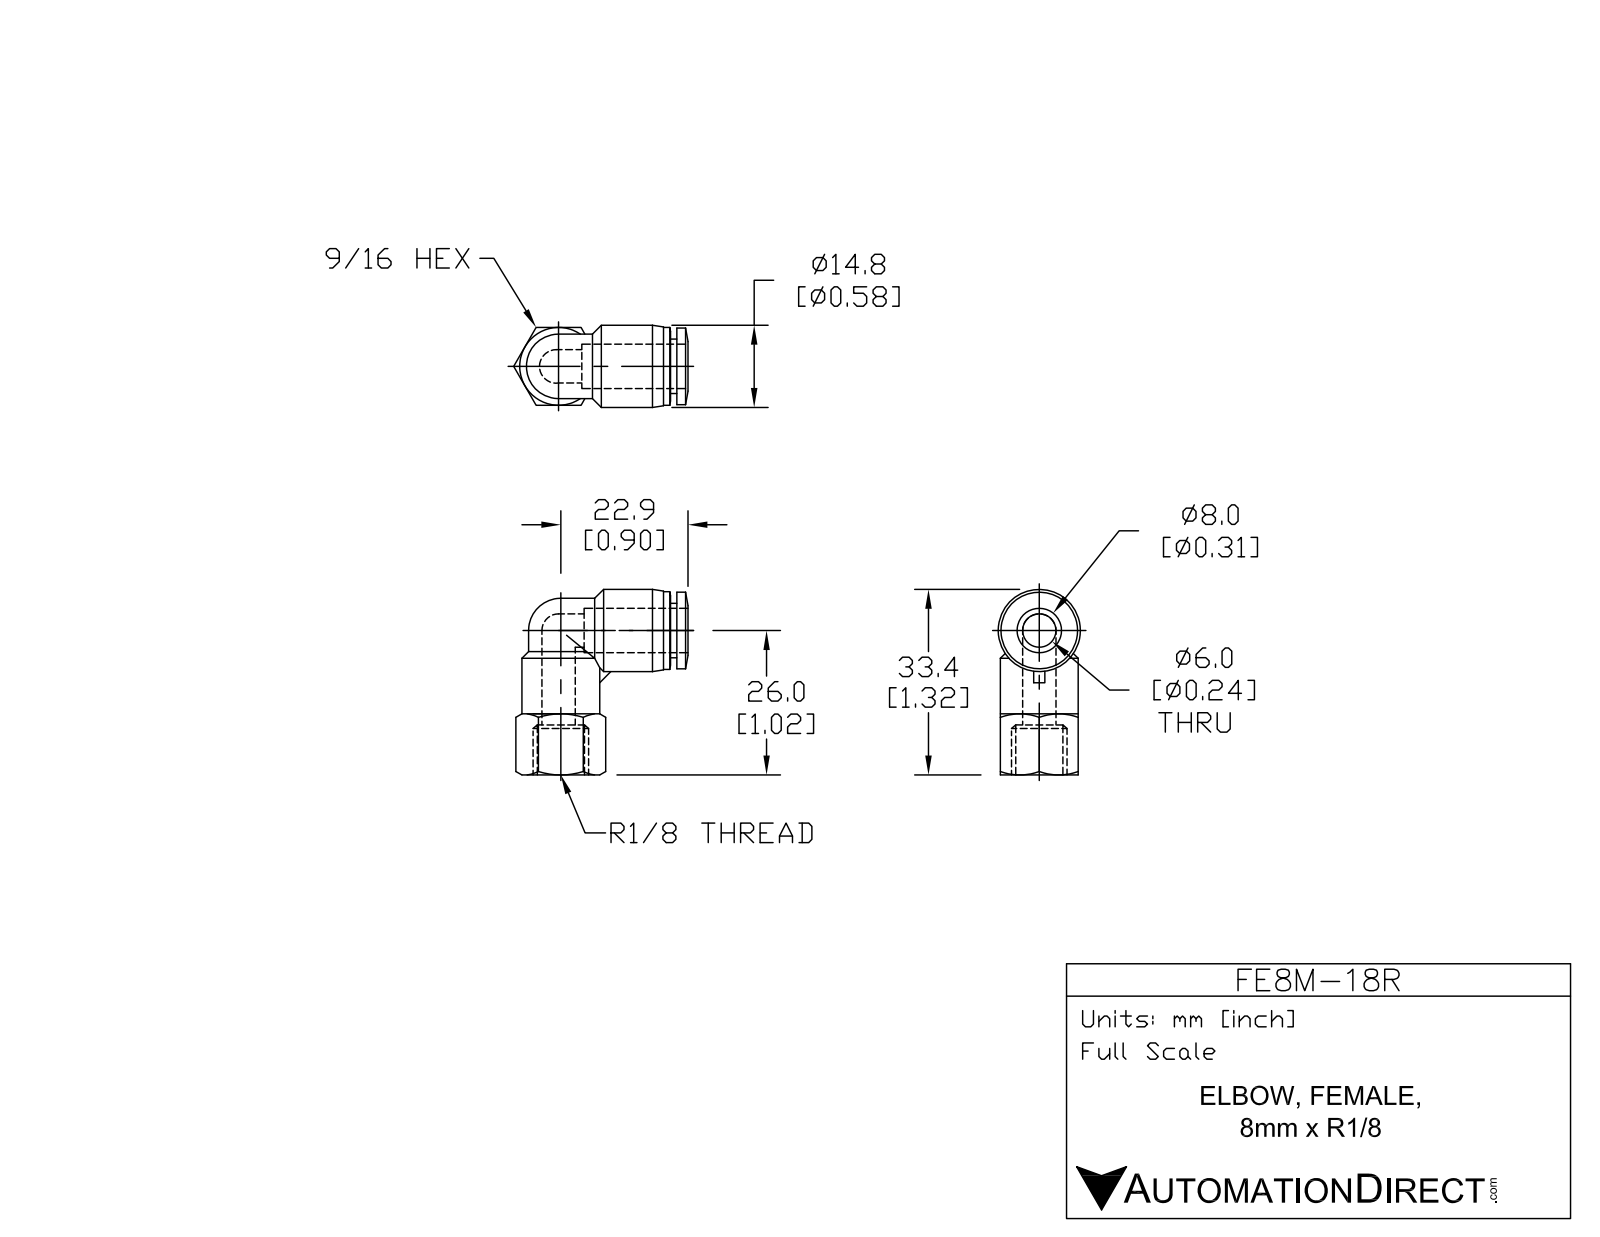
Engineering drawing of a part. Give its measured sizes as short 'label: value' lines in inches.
name: FE8M-18R
written by: SolidWorks 2015 (AUTOMOTIVE_DESIGN)
unit: in
bodies: 1 solid, 66 faces (16 planar, 19 cylindrical, 31 other)
size: 1.315 × 1.22 × 0.583
volume: 0.301 in³; area: 5.667 in²
holes: 2× ⌀0.236, 1× ⌀0.327
bosses: 2× ⌀0.551, 1× ⌀0.583, 1× ⌀0.543, 1× ⌀0.457, 1× ⌀0.386
rounds: 1× R0.228
face distances: 0.551, 0.045, 0.354, 0.596, 0.642, 0.079, 0.72, 0.124, 0.236, 0.315
